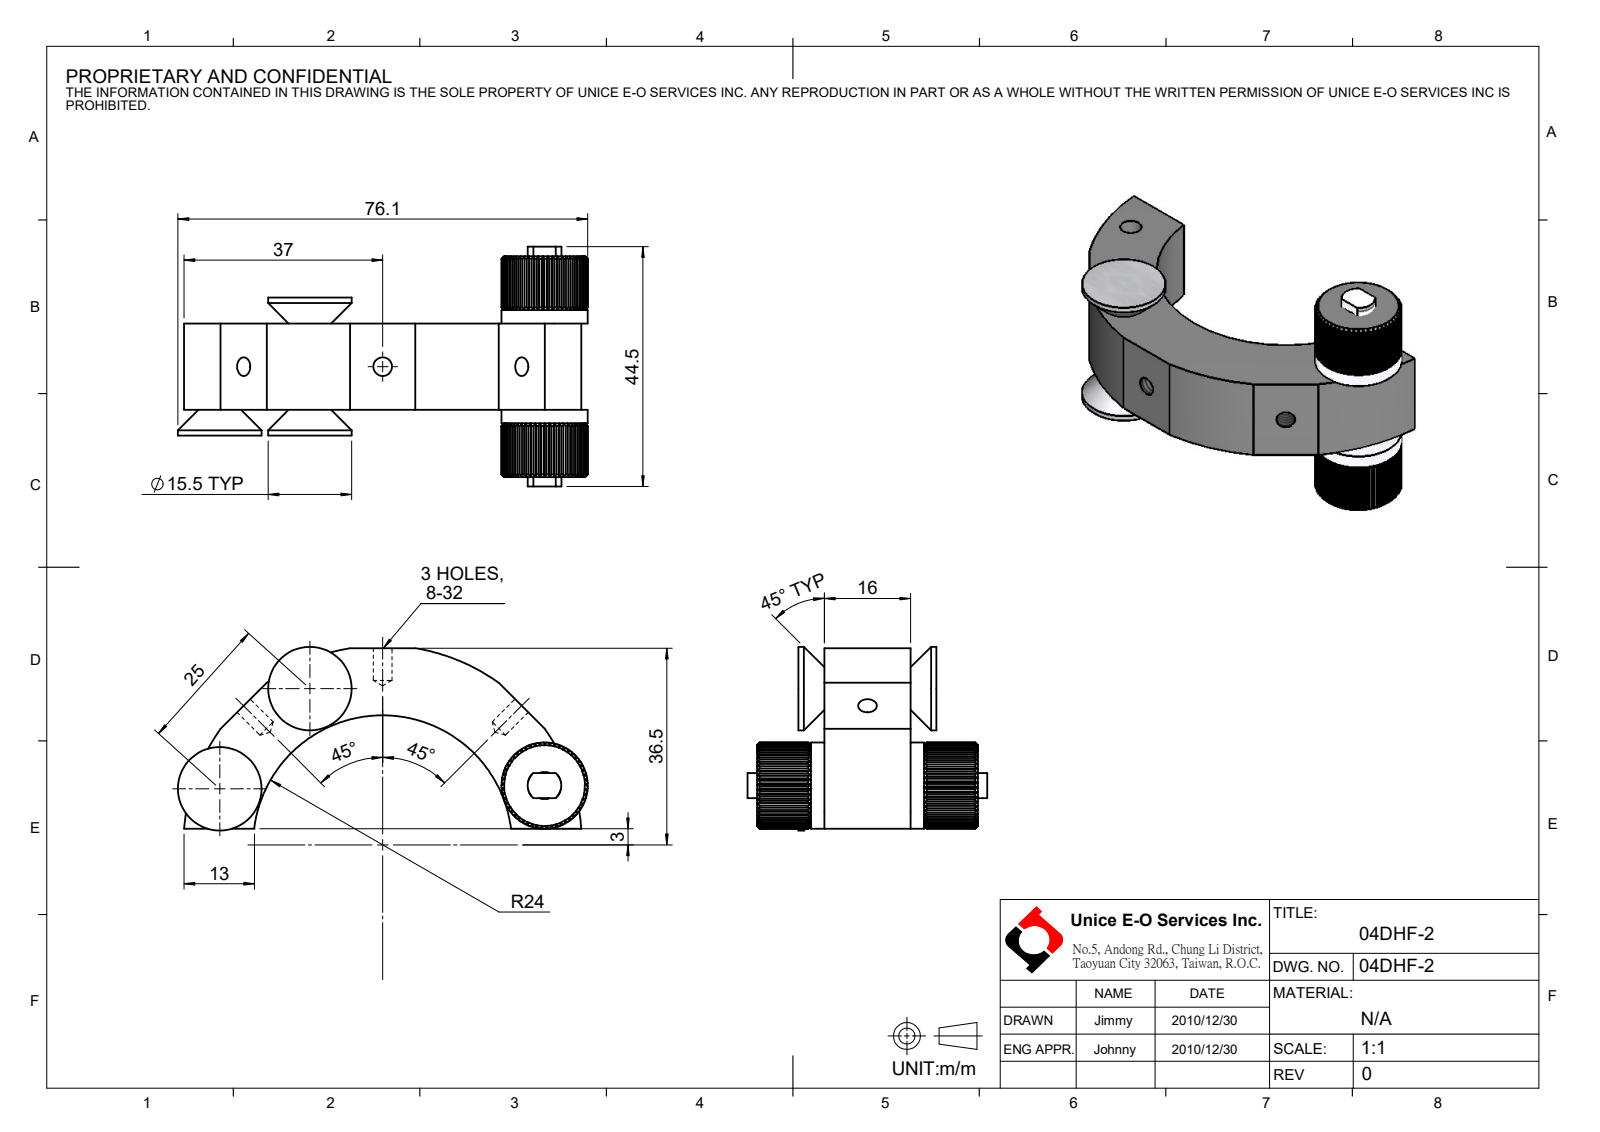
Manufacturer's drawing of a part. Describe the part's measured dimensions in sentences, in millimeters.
The part is named "04DHF-2". Its 3-D file was written by "SolidWorks 2016 (CONFIG_CONTROL_DESIGN)". It is 9 solids with 653 faces: 260 planar, 161 cylindrical and 232 other. Overall it measures 76.06 by 44.5 by 34.08 millimeters. Its volume is 24 829 cubic millimeters and its surface area 13 106 square millimeters. Round holes: 3 of diameter 3.45, 1 of diameter 4, 1 of diameter 5, 1 of diameter 6.25, 1 of diameter 6.4, 1 of diameter 10. Round bosses or shafts: 2 of diameter 15.5, 1 of diameter 16, 1 of diameter 8.1, 1 of diameter 4. Partial cylindrical surfaces (rounded edges, fillets, slot ends): 1 of radius 24, 1 of radius 37. The main face-to-face distances are 16, 4.8, 20.8, 2.5, 18.5, 2.3, 23.3, 7.7, 10, 12.5. The hole center spacings are 60.31.
